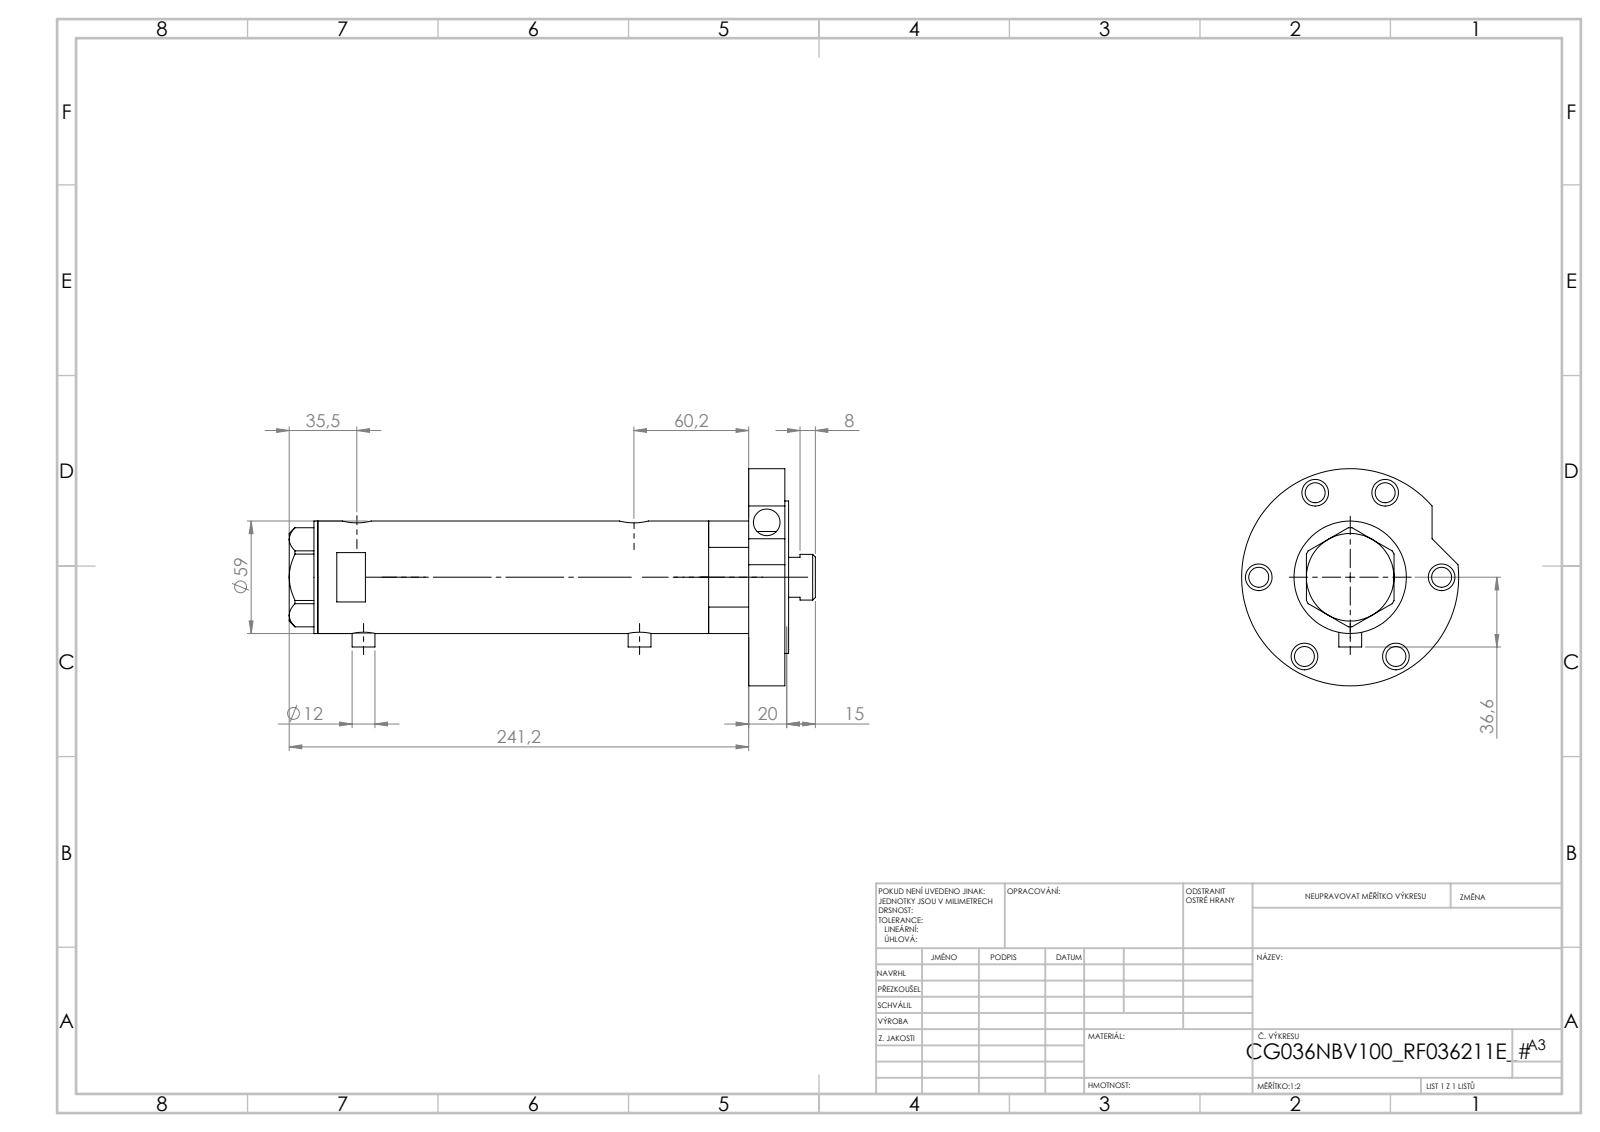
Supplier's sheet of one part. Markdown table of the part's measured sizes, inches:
| quantity | value |
| --- | --- |
| part name | V270CG_VC; V270CG_BACK; V270CG_FRONT; V270CG_RF211E (+1 more) |
| STEP written by | SolidWorks 2019 (CONFIG_CONTROL_DESIGN) |
| units | inches |
| bodies | 5 solids, 170 faces (64 planar, 86 cylindrical, 20 other) |
| overall size | 10.371 × 4.488 × 4.488 |
| volume | 44.43 in³ |
| surface area | 237.2 in² |
| round holes (diameter × count) | 0.551 × 7, 0.413 × 6, 0.197 × 2, 0.383 × 2, 0.492 × 2, 0.591 × 2, 0.335 × 1, 0.984 × 1, 1.043 × 1, 1.417 × 1, 1.575 × 1, 1.89 × 1 |
| round bosses / shafts (diameter × count) | 0.472 × 2, 4.488 × 1, 3.15 × 1, 2.323 × 1, 1.811 × 1, 0.945 × 1 |
| main face-to-face distances | 0.748, 0.827, 0.078, 8.301, 9.049, 9.128, 6.194, 2.106, 2.855, 2.933 |
| hole center spacings | 1.89, 0.114, 0.138, 2.1, 3.143, 3.273, 3.39, 3.772 |
